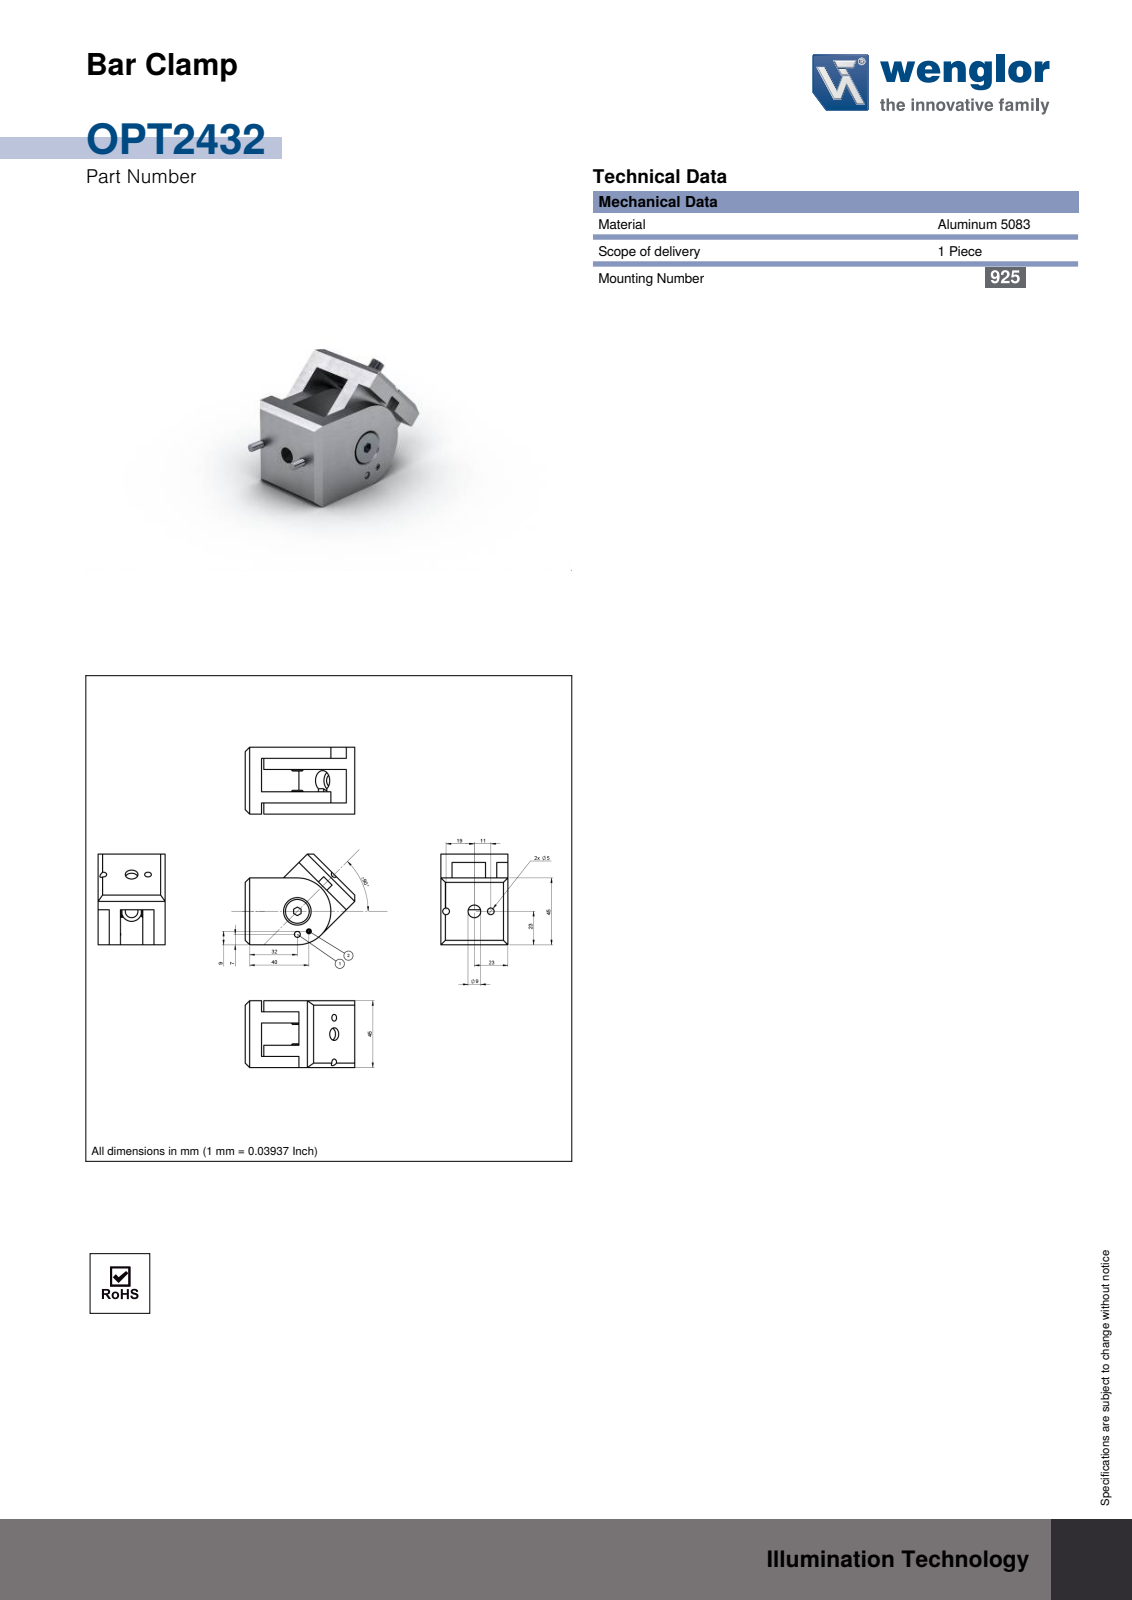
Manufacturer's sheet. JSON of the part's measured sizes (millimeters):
{"part_name": "OPT2432", "step_written_by": "SolidWorks 2021 (AUTOMOTIVE_DESIGN)", "units": "millimeters", "bodies": {"solids": 6, "faces": 139, "planar": 75, "cylindrical": 39, "other": 25}, "overall_size": [73.5, 61, 45], "volume_mm3": 94800, "surface_area_mm2": 32060, "round_holes": [[4.5, 4], [8.5, 3], [3.3, 2], [4, 2], [13.5, 2], [1.5, 1], [6.8, 1]], "round_bosses_or_shafts": [[45, 1], [16, 1], [8, 1], [3, 1]], "partial_cylinders_radius": [[0.5, 4], [4, 4]], "face_to_face_distances": [7.5, 30, 15, 37.5, 22.5, 45, 11, 45, 3, 16], "hole_center_spacings": [4, 11, 15.5, 15.5, 19, 30, 4, 8]}
